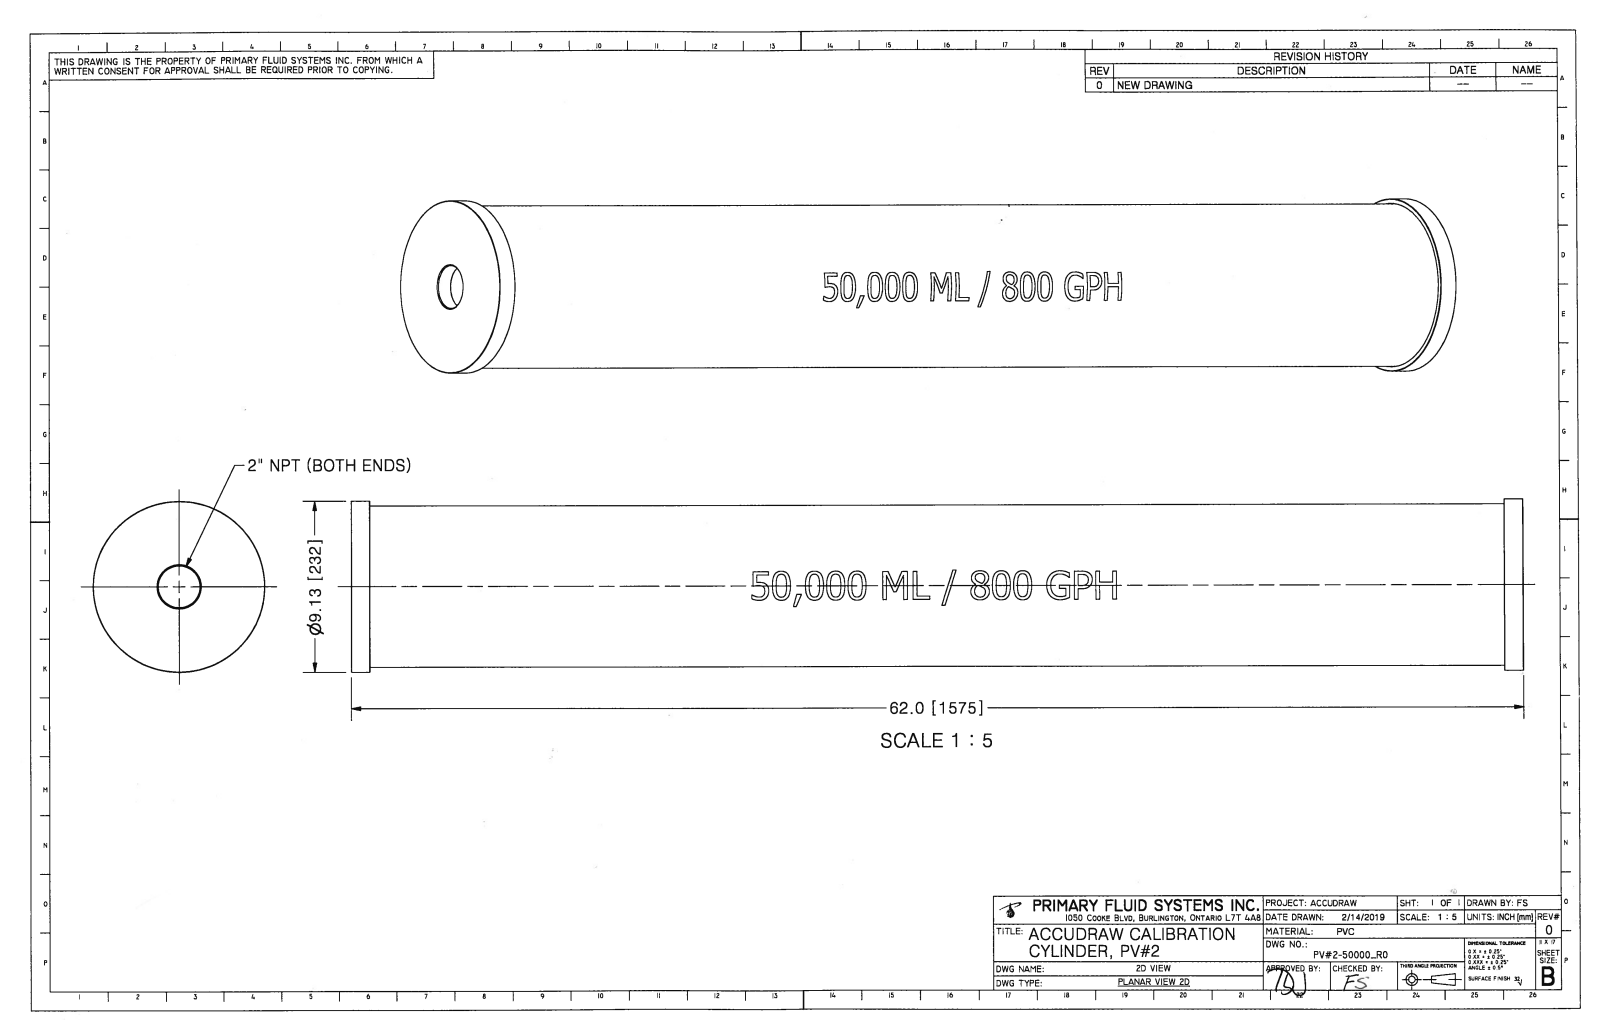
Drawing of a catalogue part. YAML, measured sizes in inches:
step_written_by: "Autodesk Inventor 2009 (AUTOMOTIVE_DESIGN)"
units: inches
bodies: {solids: 1, faces: 243, planar: 65, cylindrical: 32, other: 146}
overall_size: [62, 9.125, 9.125]
volume: 388.8
surface_area: 3587
round_holes:
  - {diameter: 8.255, count: 1}
  - {diameter: 8.654, count: 1}
round_bosses_or_shafts:
  - {diameter: 9.125, count: 1}
  - {diameter: 8.599, count: 1}
  - {diameter: 8.217, count: 1}
partial_cylinders:
  - {radius: 4.299, count: 1}
face_to_face_distances: [62, 61, 1, 60, 0.5, 61.5, 60.5, 0.2, 9.639, 8.502]
